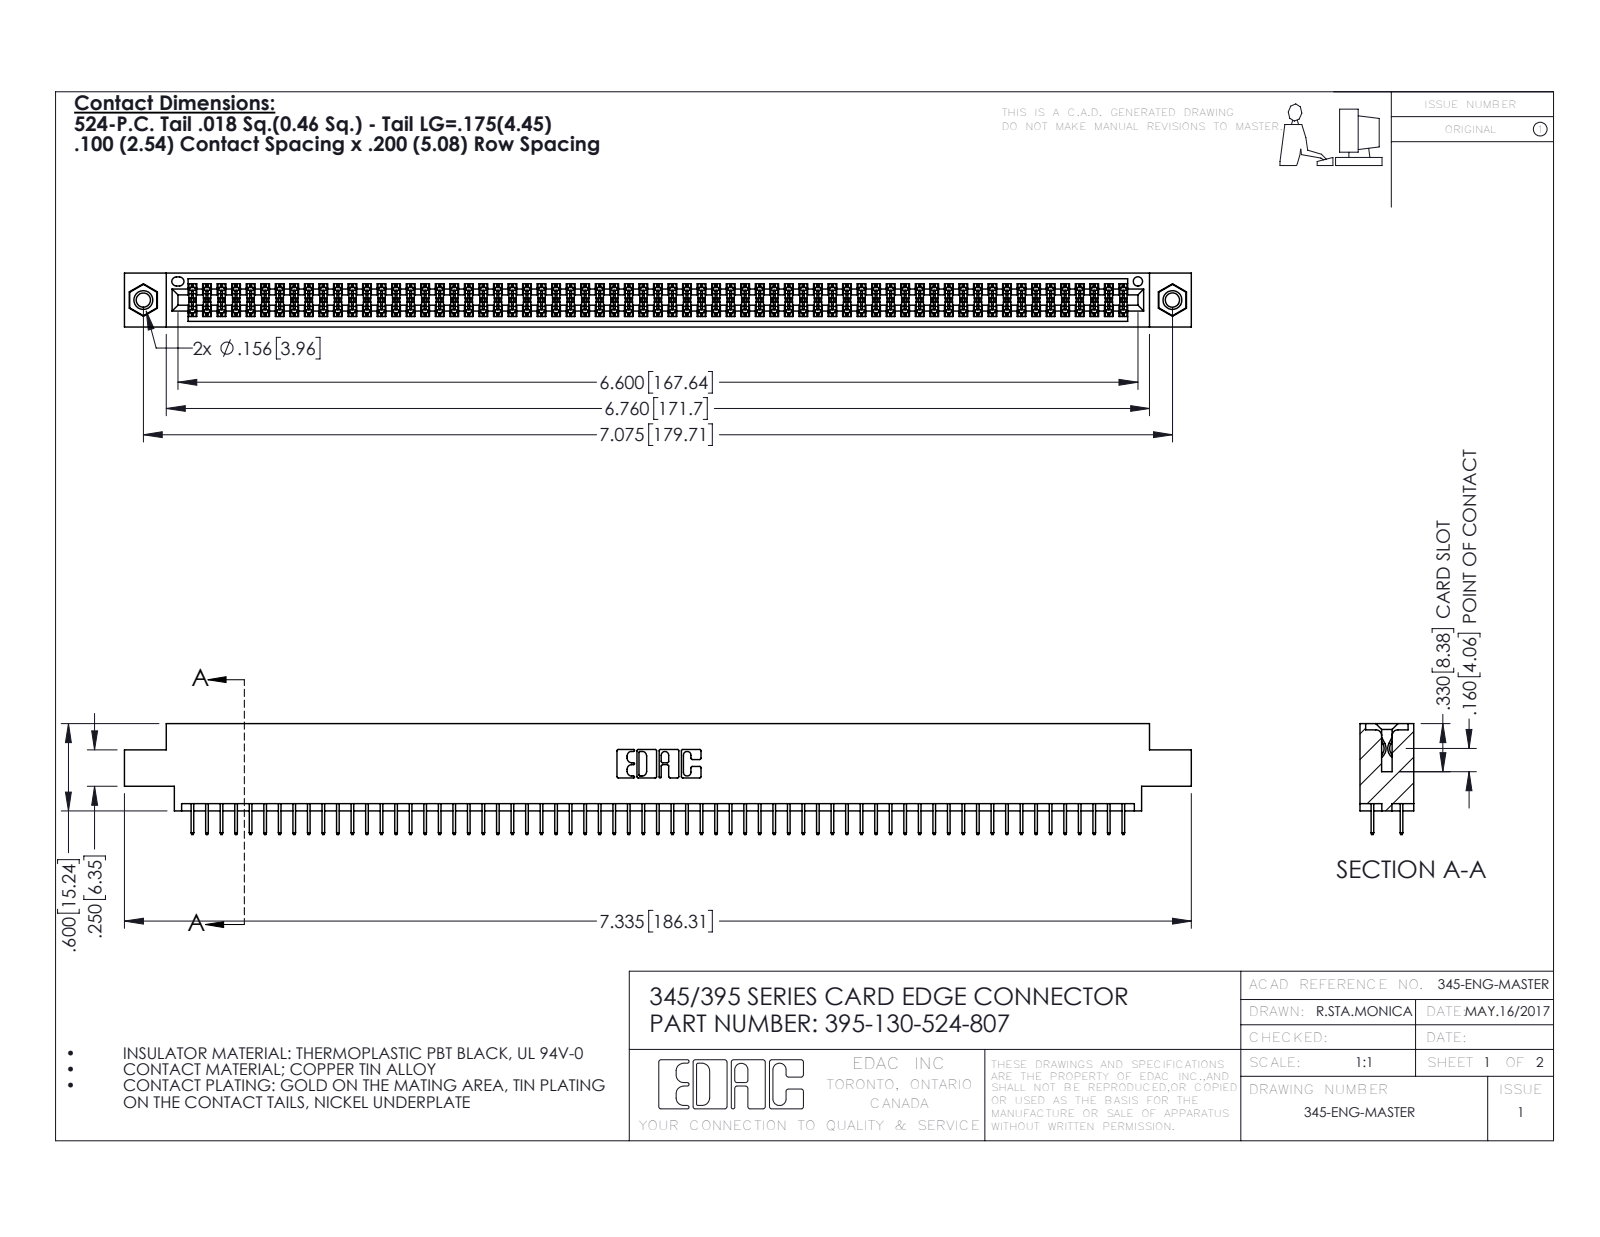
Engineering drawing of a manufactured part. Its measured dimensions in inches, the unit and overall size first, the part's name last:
Units: inches
Overall size (bounding box): 7.335 × 0.762 × 0.37
Round holes (diameter × count): ⌀0.098 ×2, ⌀0.125 ×2, ⌀0.156 ×2, ⌀0.064 ×1
Round bosses / shafts (diameter × count): ⌀0.155 ×2
Partial cylindrical surfaces — rounded edges, fillets, slot ends (radius × count): R0.006 ×195, R0.01 ×22, R0.007 ×6, R0.031 ×6, R0.026 ×3, R0.014 ×2, R0.019 ×2, R0.022 ×2
Main face-to-face distances: 0.072, 0.298, 0.2, 0.37, 0.098, 0.272, 0.025, 0.225, 0.072, 0.175
Hole centre spacings: 0.27, 6.839, 7.075
Volume: 1.098 in³ · Surface area: 41.36 in²
Bodies: 133 solids, 7210 faces (5186 planar, 2008 cylindrical, 16 other)
Part name (STEP PRODUCT): 395-130-524-807; 345 Part_0.170 Offset - 0.156 Dia-TI; 345-250-001_345-250-005-103; 345-292-001_345-293-124
STEP written by: SolidWorks 2016 (CONFIG_CONTROL_DESIGN)
